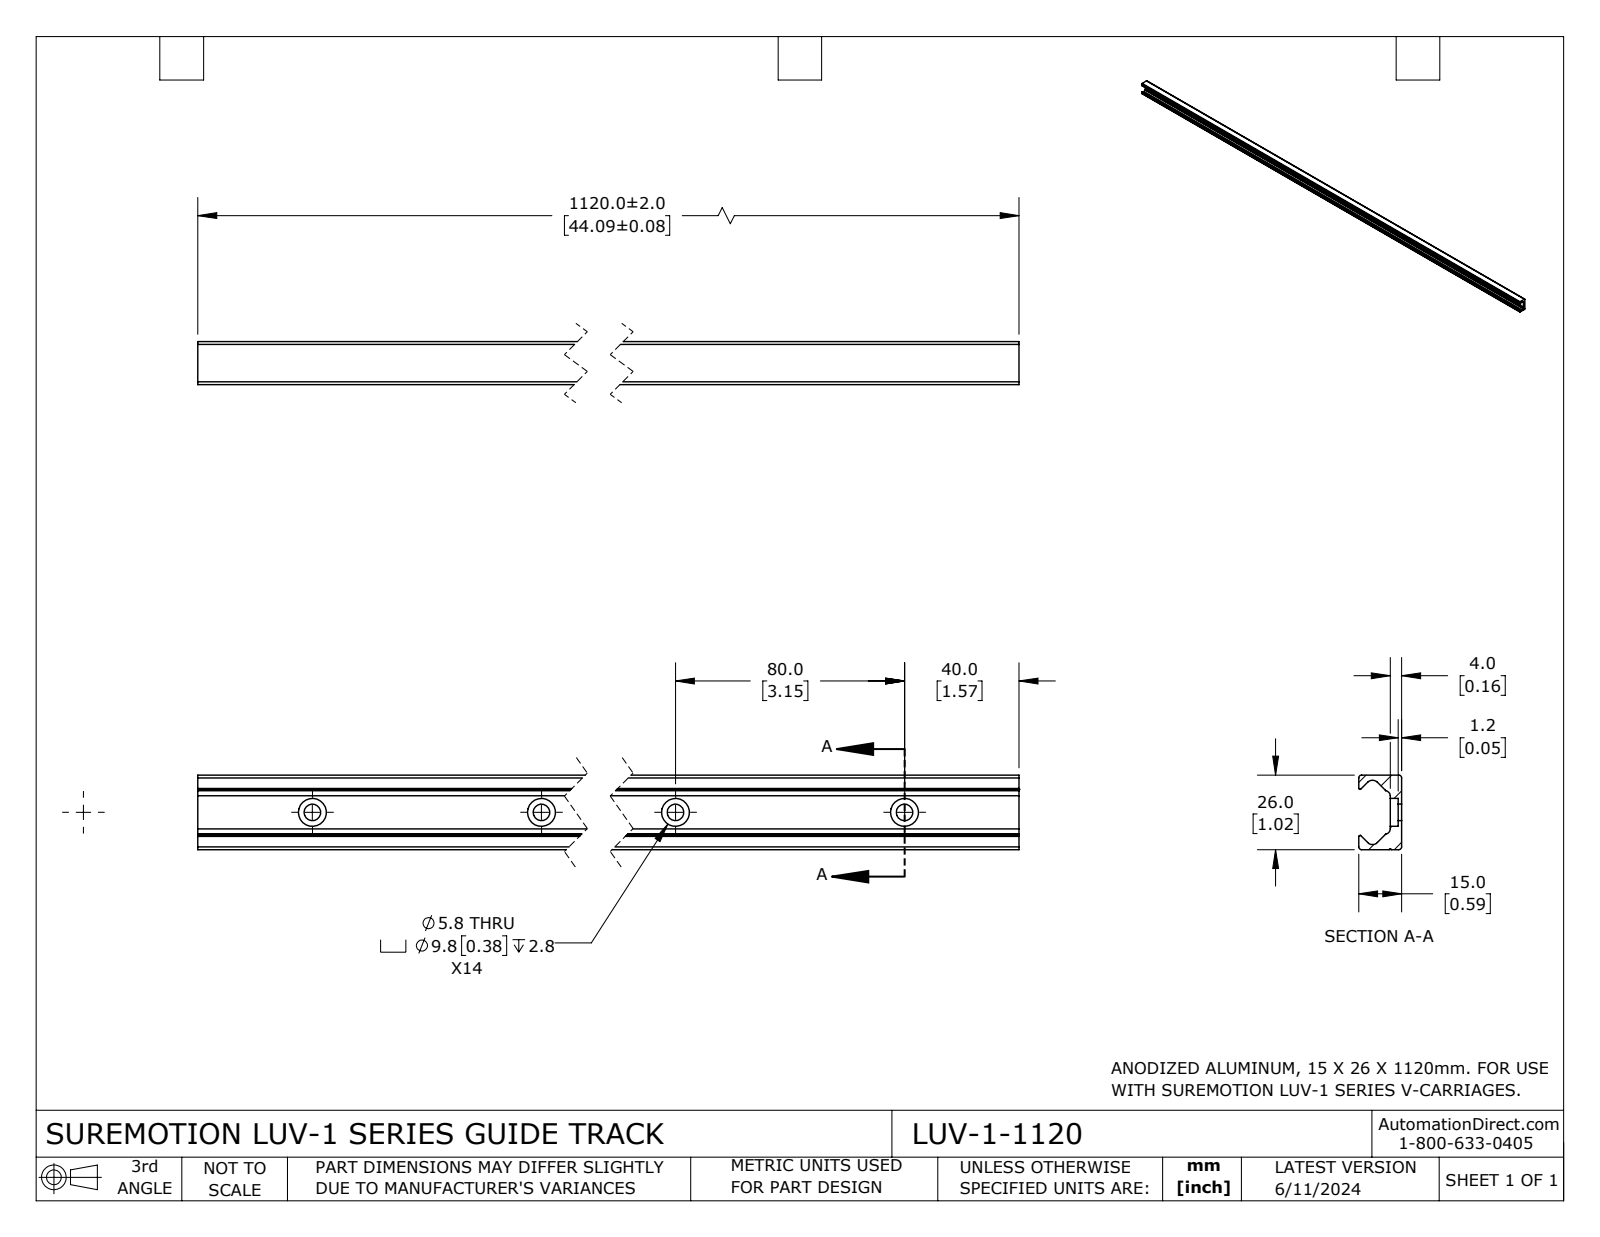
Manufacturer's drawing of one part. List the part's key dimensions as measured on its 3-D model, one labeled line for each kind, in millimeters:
Part name (STEP PRODUCT): LUV-1-1120
STEP written by: SolidWorks 2023 (CONFIG_CONTROL_DESIGN)
Units: millimetres
Bodies: 1 solid, 98 faces (27 planar, 71 cylindrical, 0 other)
Overall size (bounding box): 1120 × 26.01 × 15.01
Volume: 201 667 mm³ · Surface area: 118 845 mm²
Round holes (diameter × count): ⌀5.79 ×14, ⌀9.75 ×14
Partial cylindrical surfaces — rounded edges, fillets, slot ends (radius × count): R0.99 ×4, R0.51 ×2, R0.64 ×2, R0.76 ×2, R1.78 ×2, R2.39 ×2, R0.33 ×1
Main face-to-face distances: 26.02, 4.01, 15.02, 11.01, 17.27, 1.21, 2.8, 13.81, 1120
Hole centre spacings: 80, 160, 240, 320, 400, 480, 560, 640
